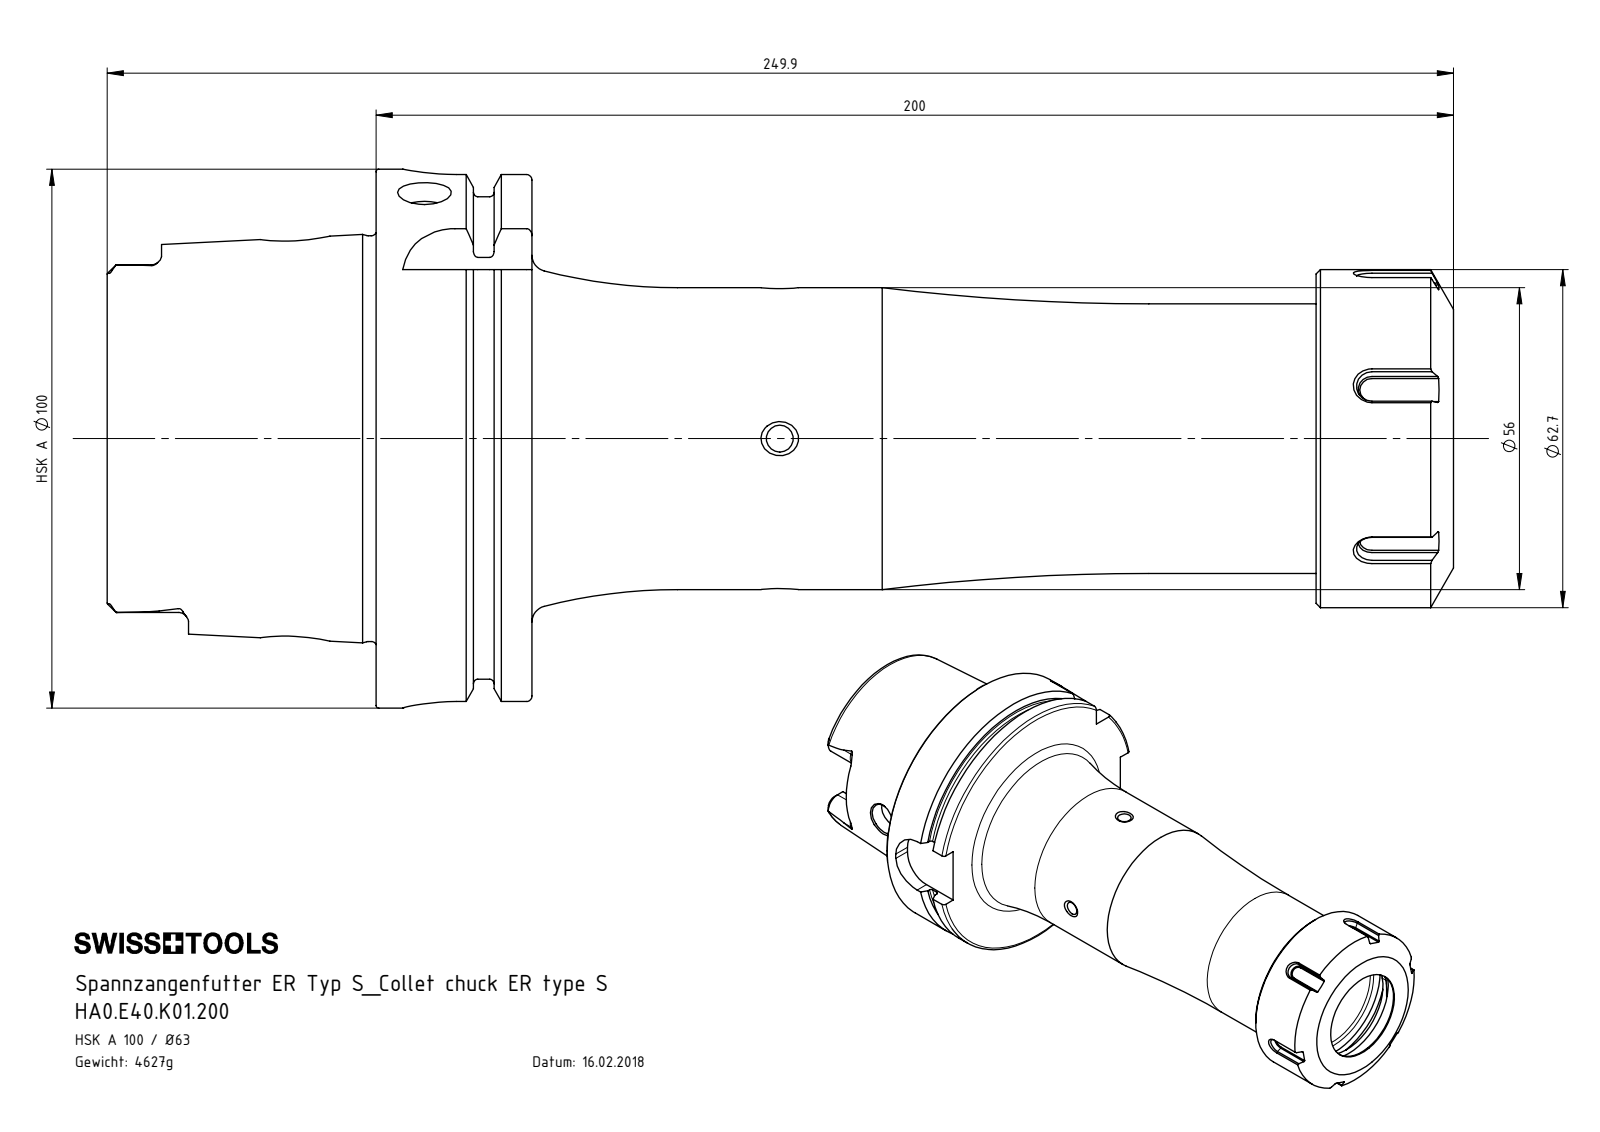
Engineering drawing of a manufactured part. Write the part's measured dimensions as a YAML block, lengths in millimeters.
part_name: "HA0.E40.K01.200; HA0-E40.K01.200_C_Fertigbearbeitung; E40-ER1.001.025; ERU-AN5.K01.020_A"
step_written_by: "SolidWorks 2017 (CONFIG_CONTROL_DESIGN)"
units: millimeters
bodies: {solids: 3, faces: 337, planar: 126, cylindrical: 81, other: 130}
overall_size: [249.9, 100, 100]
volume: 589467
surface_area: 97197
round_holes:
  - {diameter: 10, count: 3}
  - {diameter: 5, count: 2}
  - {diameter: 12, count: 2}
  - {diameter: 6, count: 1}
  - {diameter: 11, count: 1}
  - {diameter: 22.5, count: 1}
  - {diameter: 26, count: 1}
  - {diameter: 30.5, count: 1}
  - {diameter: 33.5, count: 1}
  - {diameter: 48.5, count: 1}
  - {diameter: 50.5, count: 1}
  - {diameter: 53, count: 1}
round_bosses_or_shafts:
  - {diameter: 100, count: 1}
  - {diameter: 91.95, count: 1}
  - {diameter: 75.26, count: 1}
  - {diameter: 62.7, count: 1}
  - {diameter: 56, count: 1}
  - {diameter: 50, count: 1}
partial_cylinders:
  - {radius: 1.9, count: 6}
  - {radius: 4.88, count: 4}
  - {radius: 10, count: 4}
  - {radius: 19.26, count: 2}
face_to_face_distances: [28.95, 12.45, 16.5, 174.5, 162.05, 145.55, 200, 187.55, 171.05, 25.5]
hole_center_spacings: [67.95, 89.95]
